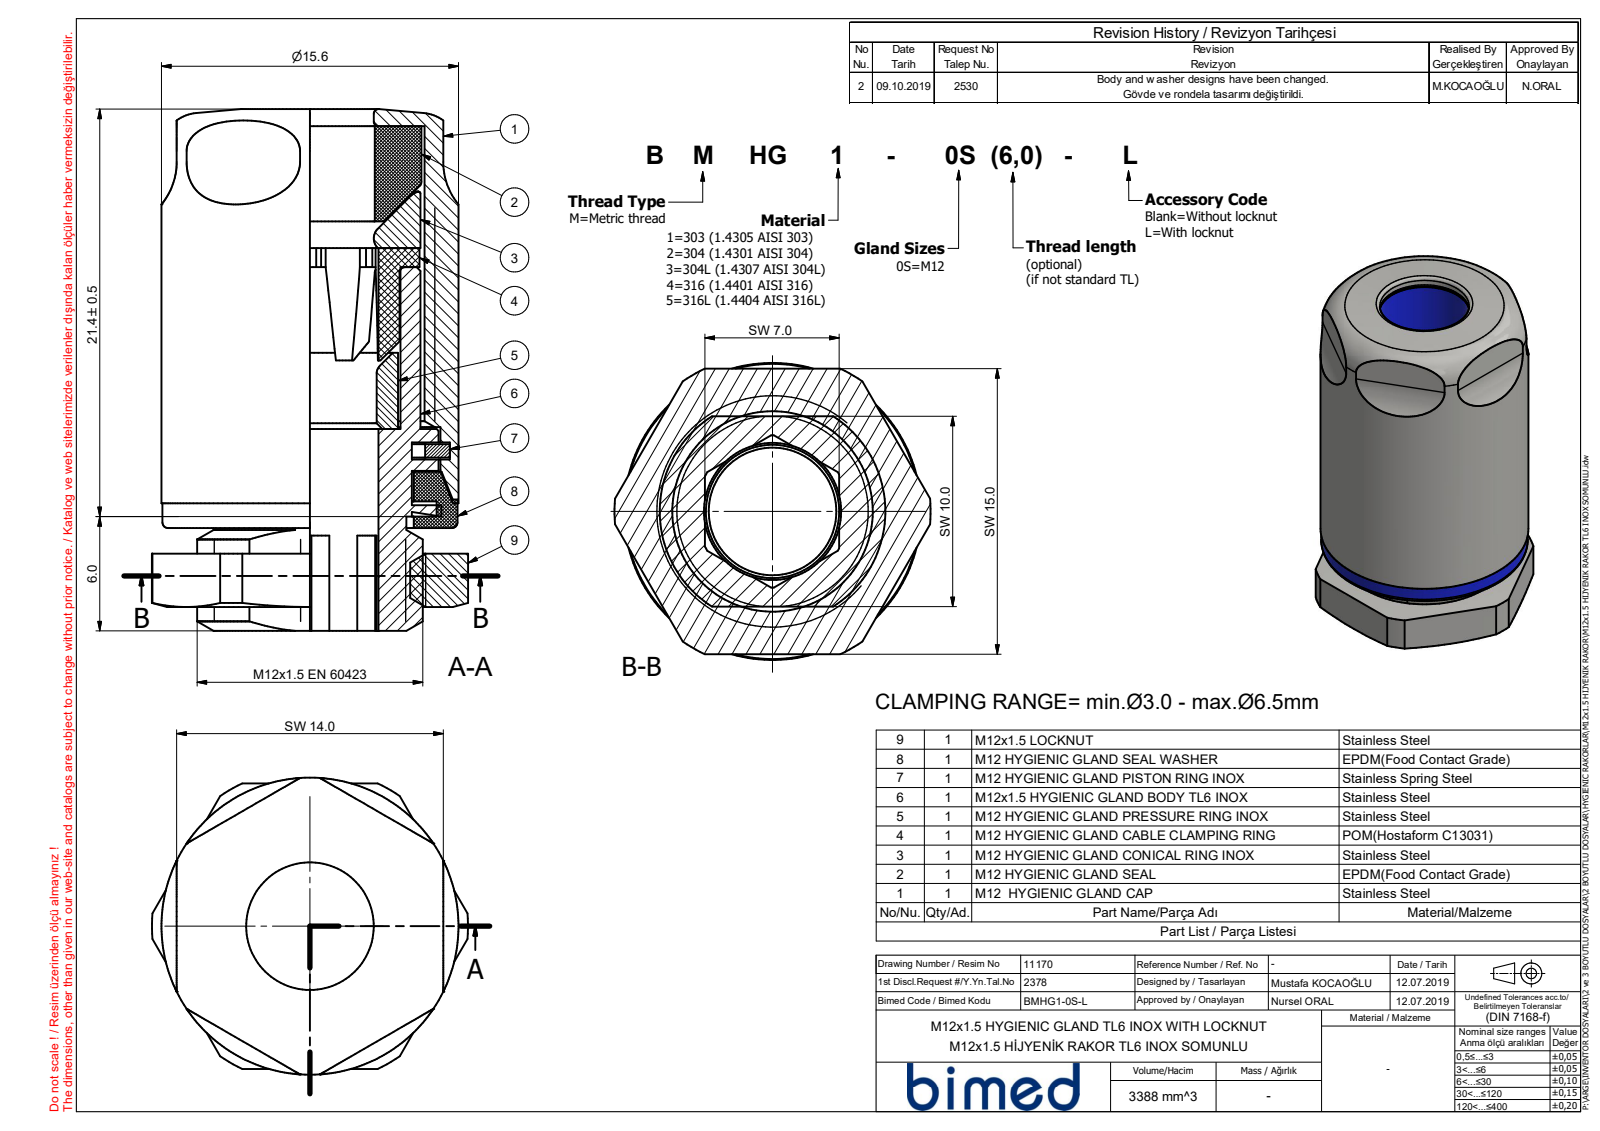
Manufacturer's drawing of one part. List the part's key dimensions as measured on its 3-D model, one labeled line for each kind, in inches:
Part name (STEP PRODUCT): BMHG1-0S-L
STEP written by: SolidWorks 2021 (CONFIG_CONTROL_DESIGN)
Units: inches
Bodies: 1 solid, 53 faces (15 planar, 16 cylindrical, 22 other)
Overall size (bounding box): 1.091 × 0.654 × 0.614
Volume: 0.301 in³ · Surface area: 2.849 in²
Round bosses / shafts (diameter × count): ⌀0.614 ×1, ⌀0.61 ×1, ⌀0.398 ×1
Partial cylindrical surfaces — rounded edges, fillets, slot ends (radius × count): R0.233 ×1, R0.327 ×1
Main face-to-face distances: 0.053, 0.159, 0.213, 0.049, 0.11, 0.163, 0.591, 0.098, 0.492, 0.394
